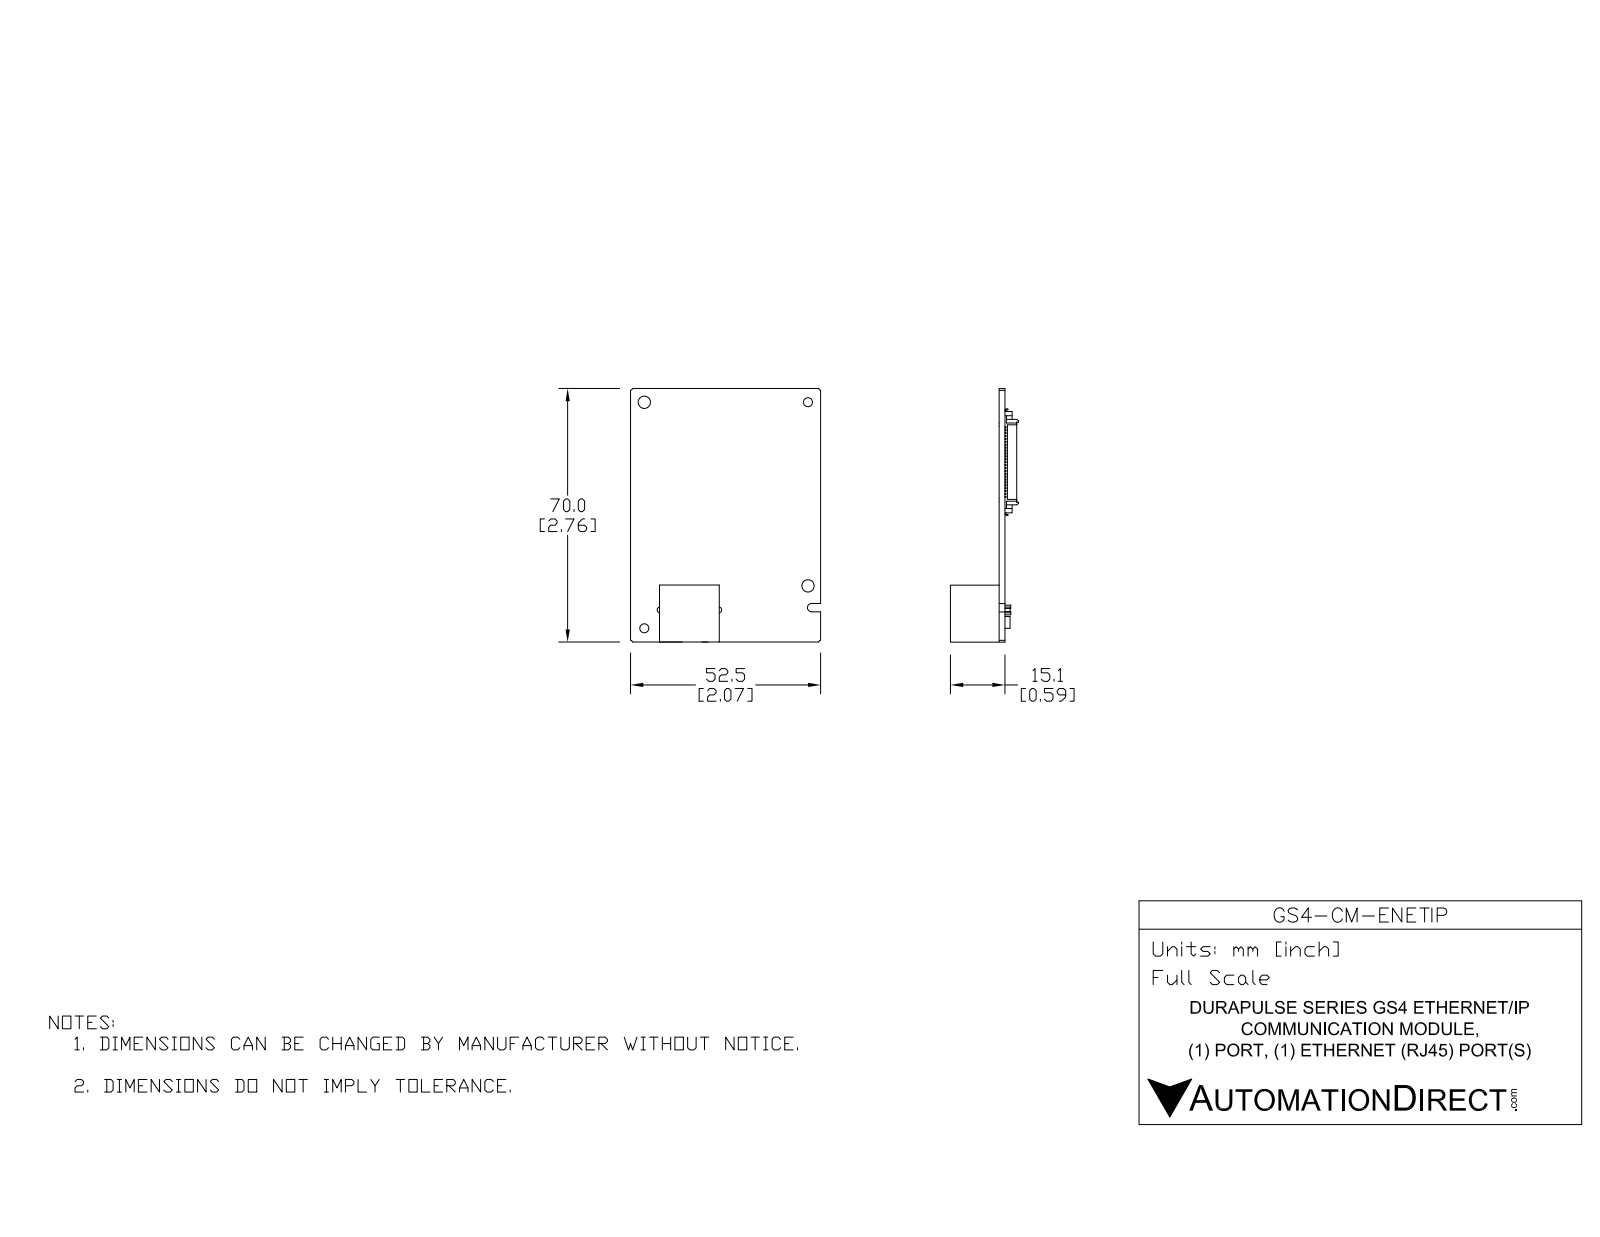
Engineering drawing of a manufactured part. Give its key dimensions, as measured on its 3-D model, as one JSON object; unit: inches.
{"part_name": "GS4-CM-ENETIP", "step_written_by": "SolidWorks 2016 (AUTOMOTIVE_DESIGN)", "units": "inches", "bodies": {"solids": 3, "faces": 580, "planar": 547, "cylindrical": 29, "other": 4}, "overall_size": [2.756, 2.067, 0.741], "volume_in3": 0.491, "surface_area_in2": 16.25, "round_holes": [[0.035, 2], [0.098, 2], [0.134, 2], [0.031, 1], [0.039, 1]], "partial_cylinders_radius": [[0.01, 4], [0.02, 4], [0.045, 1]], "face_to_face_distances": [0.063, 0.563, 0.593, 0.53, 0.098, 0.65, 0.62, 0.087, 0.161, 0.157], "hole_center_spacings": [0.322, 0.815, 0.936, 1.094, 1.616, 1.743, 1.78, 1.838]}
